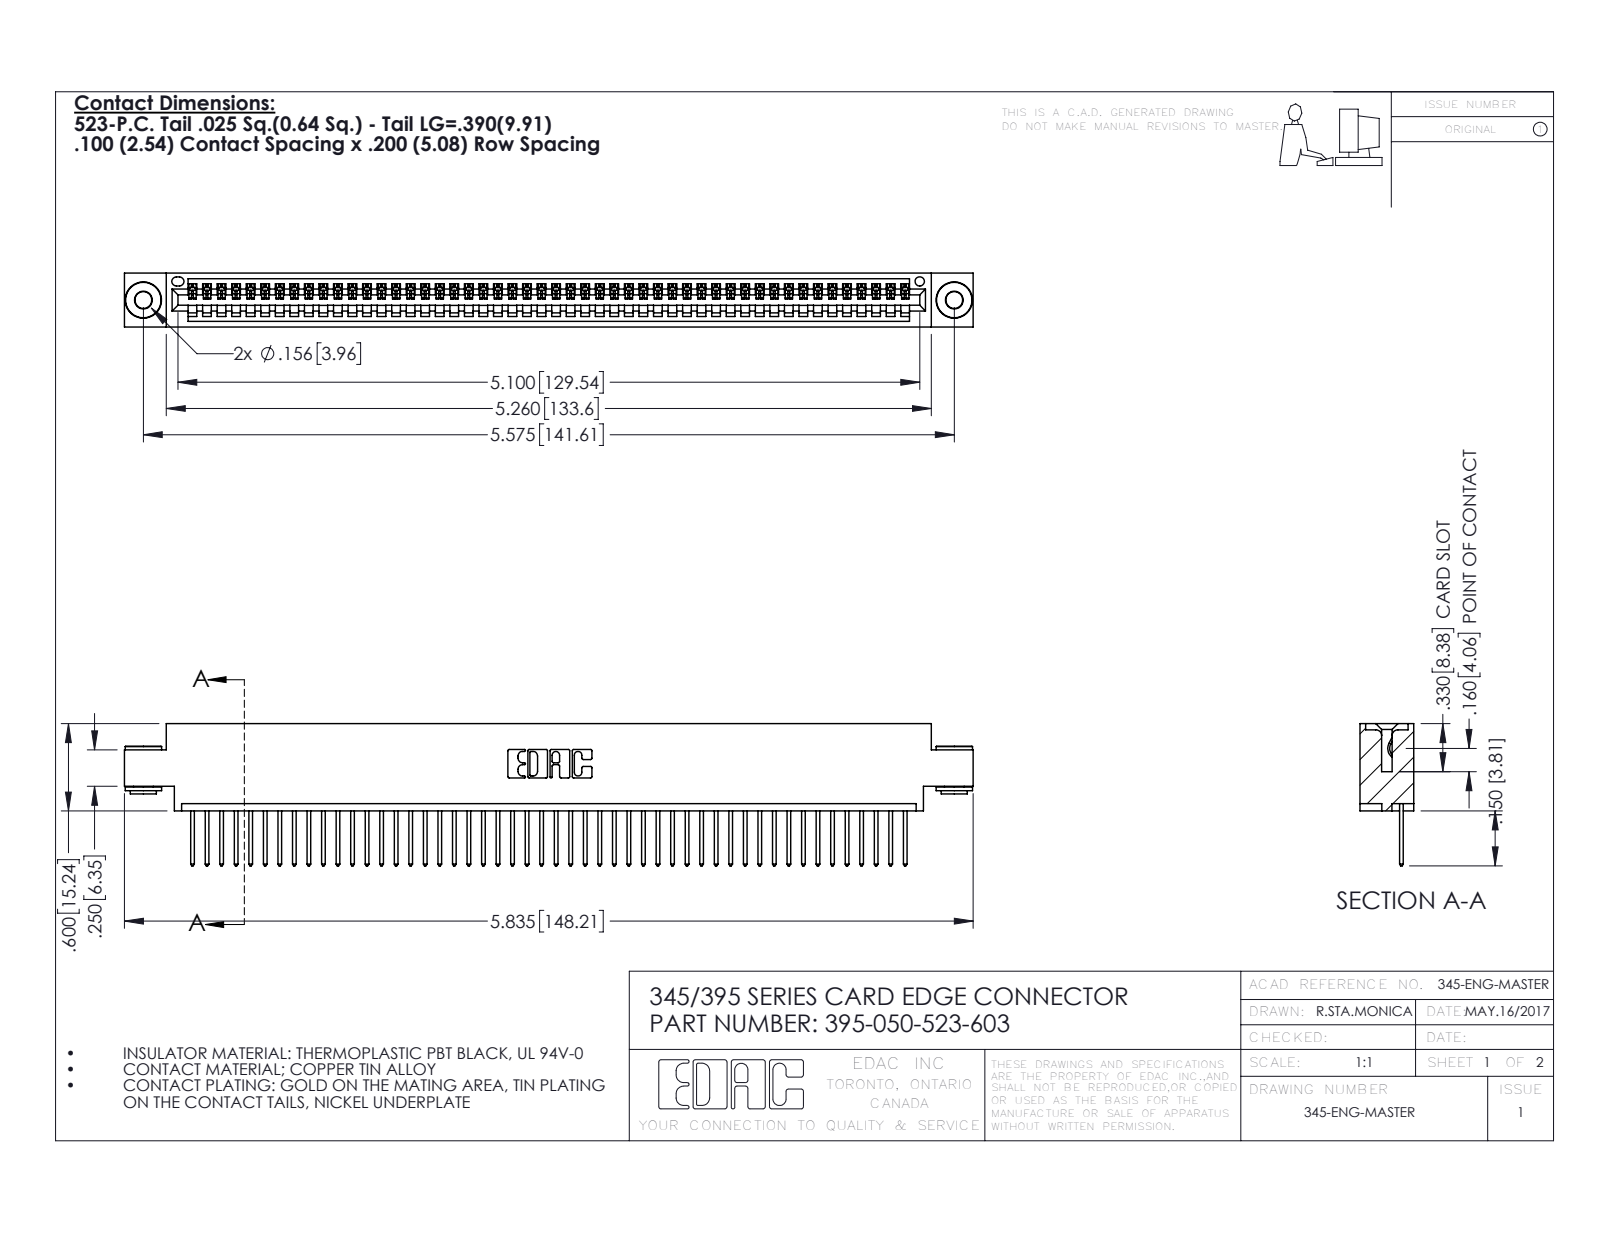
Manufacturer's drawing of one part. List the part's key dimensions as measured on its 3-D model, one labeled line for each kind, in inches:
Part name (STEP PRODUCT): 345-292-001_345-293-123; 345 Part_0.170 Offset - 0.156 Dia-TH; 345-250-002_345-250-002-102; 395-050-523-603
STEP written by: SolidWorks 2016 (CONFIG_CONTROL_DESIGN)
Units: inches
Bodies: 53 solids, 3068 faces (2094 planar, 966 cylindrical, 8 other)
Overall size (bounding box): 5.835 × 0.977 × 0.37
Volume: 0.856 in³ · Surface area: 29.68 in²
Round holes (diameter × count): ⌀0.116 ×2, ⌀0.156 ×2, ⌀0.064 ×1
Round bosses / shafts (diameter × count): ⌀0.25 ×2, ⌀0.18 ×2, ⌀0.136 ×2
Partial cylindrical surfaces — rounded edges, fillets, slot ends (radius × count): R0.006 ×100, R0.01 ×100, R0.01 ×22, R0.007 ×6, R0.031 ×6, R0.026 ×3, R0.031 ×2, R0.04 ×2
Main face-to-face distances: 0.072, 0.298, 0.37, 0.098, 0.272, 0.025, 0.2, 0.225, 0.175, 0.149
Hole centre spacings: 0.27, 5.339, 5.575
